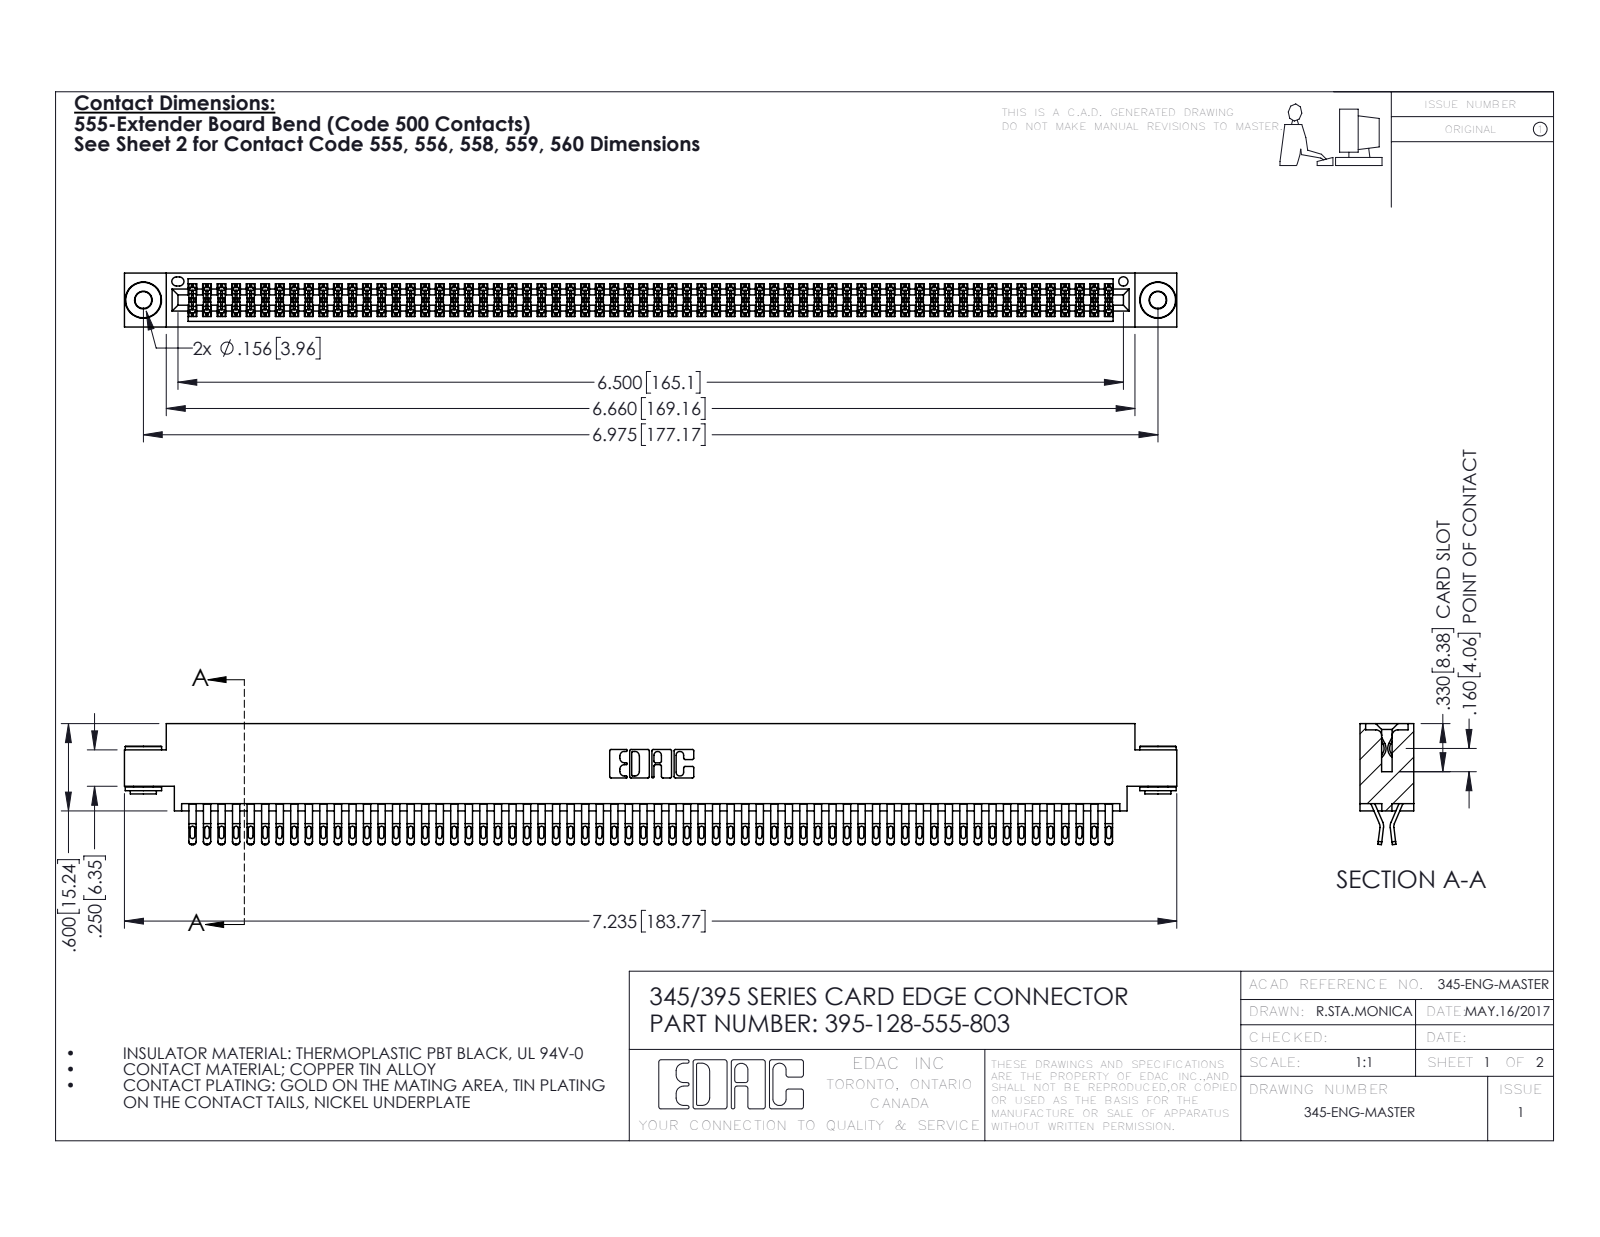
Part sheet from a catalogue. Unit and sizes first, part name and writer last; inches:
Units: inches
Overall size (bounding box): 7.235 × 0.832 × 0.37
Round holes (diameter × count): ⌀0.116 ×2, ⌀0.156 ×2, ⌀0.064 ×1
Round bosses / shafts (diameter × count): ⌀0.25 ×2, ⌀0.18 ×2, ⌀0.136 ×2
Partial cylindrical surfaces — rounded edges, fillets, slot ends (radius × count): R0.016 ×320, R0.02 ×256, R0.006 ×192, R0.01 ×22, R0.007 ×6, R0.031 ×6, R0.026 ×3, R0.01 ×2
Main face-to-face distances: 0.072, 0.298, 0.37, 0.025, 0.2, 0.098, 0.272, 0.225, 0.175, 0.149
Hole centre spacings: 0.27, 6.739, 6.975
Volume: 1.119 in³ · Surface area: 45.21 in²
Bodies: 131 solids, 7336 faces (4062 planar, 3266 cylindrical, 8 other)
Part name (STEP PRODUCT): 395-128-555-803; 345-292-001_555 Tail; 345-250-002_345-250-002-102; 345 Part_0.170 Offset - 0.156 Dia-TH
STEP written by: SolidWorks 2016 (CONFIG_CONTROL_DESIGN)
